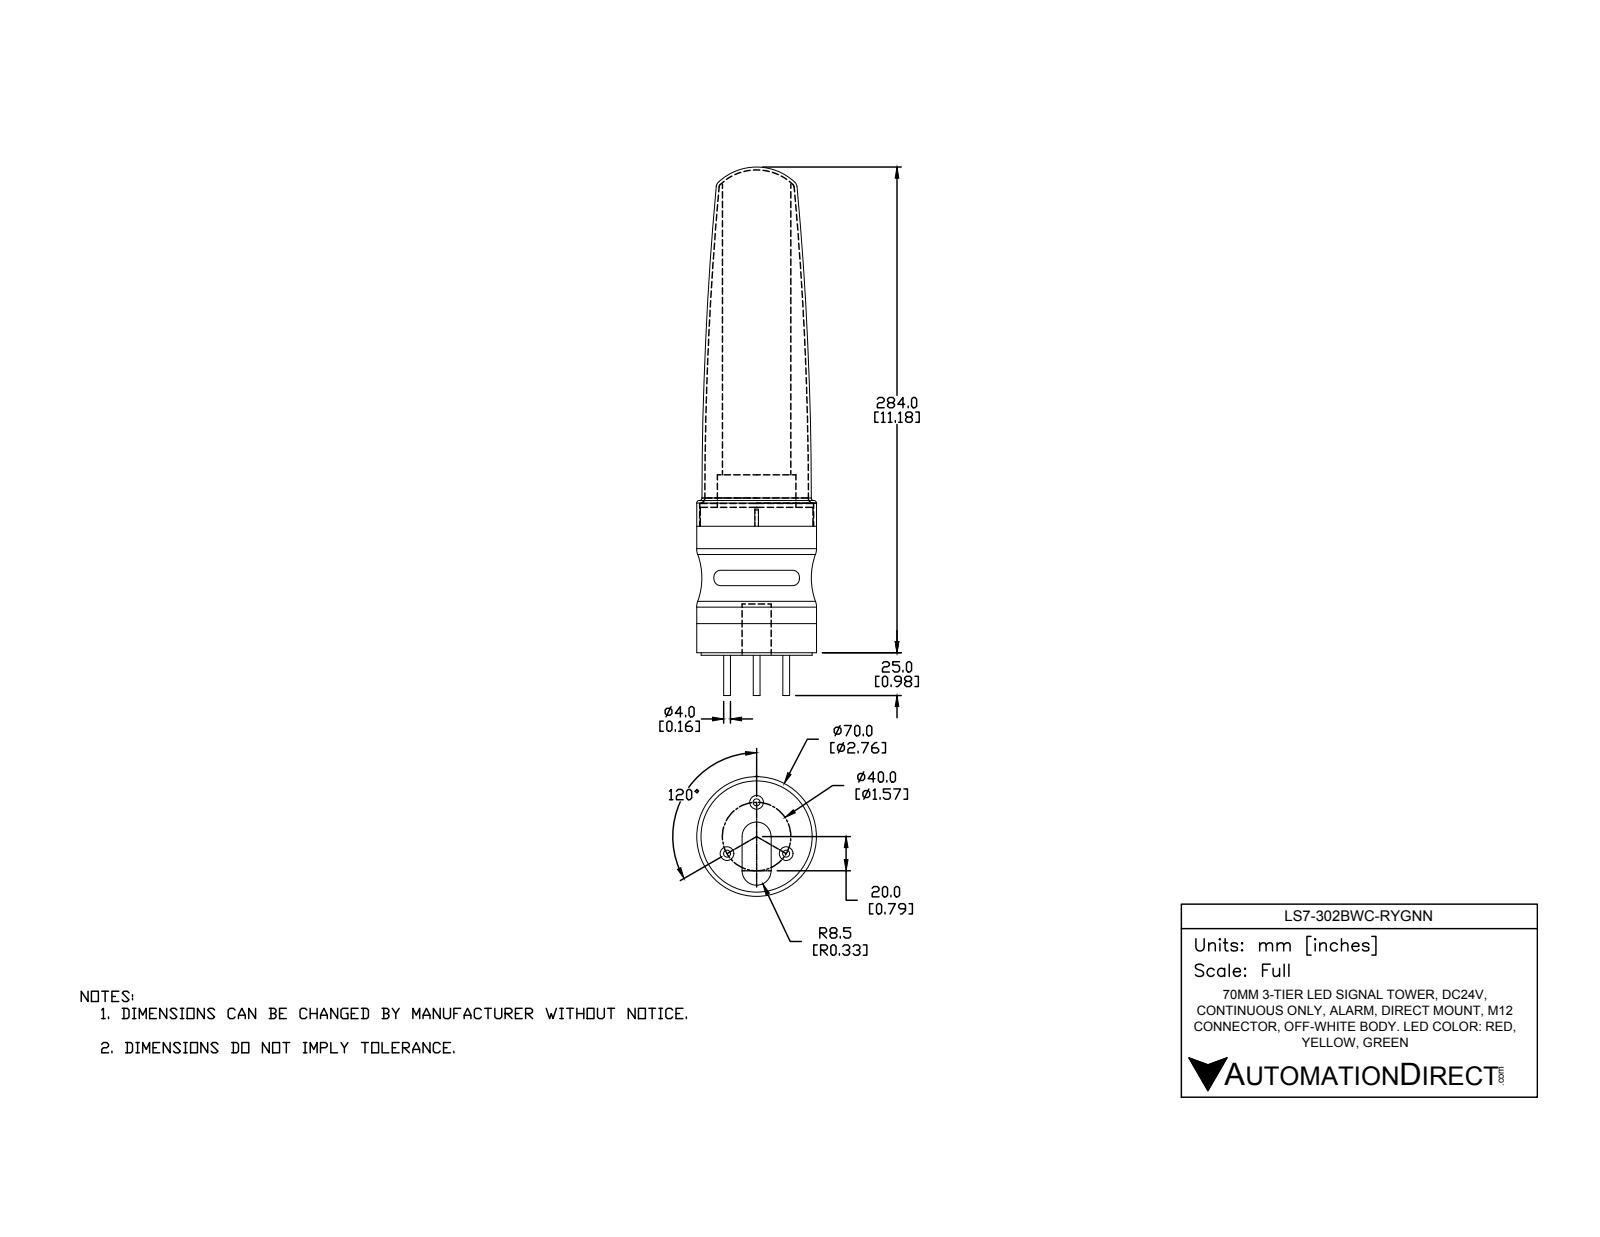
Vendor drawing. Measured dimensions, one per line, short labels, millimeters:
name: LS7-302BWC-RYGNN
written by: SolidWorks 2016 (AUTOMOTIVE_DESIGN)
unit: mm
bodies: 8 solids, 101 faces (32 planar, 45 cylindrical, 24 other)
size: 309 × 70.3 × 70
volume: 595 853 mm³; area: 148 747 mm²
holes: 3× ⌀8, 1× ⌀66.6
bosses: 3× ⌀4, 1× ⌀70, 1× ⌀66, 1× ⌀65, 1× ⌀46, 1× ⌀40
rounds: 4× R4, 2× R8.5, 1× R1, 1× R2
face distances: 17, 104, 87, 1.5, 18.5, 105.5, 86.5, 85, 68, 19
hole spacings: 20, 34.64
